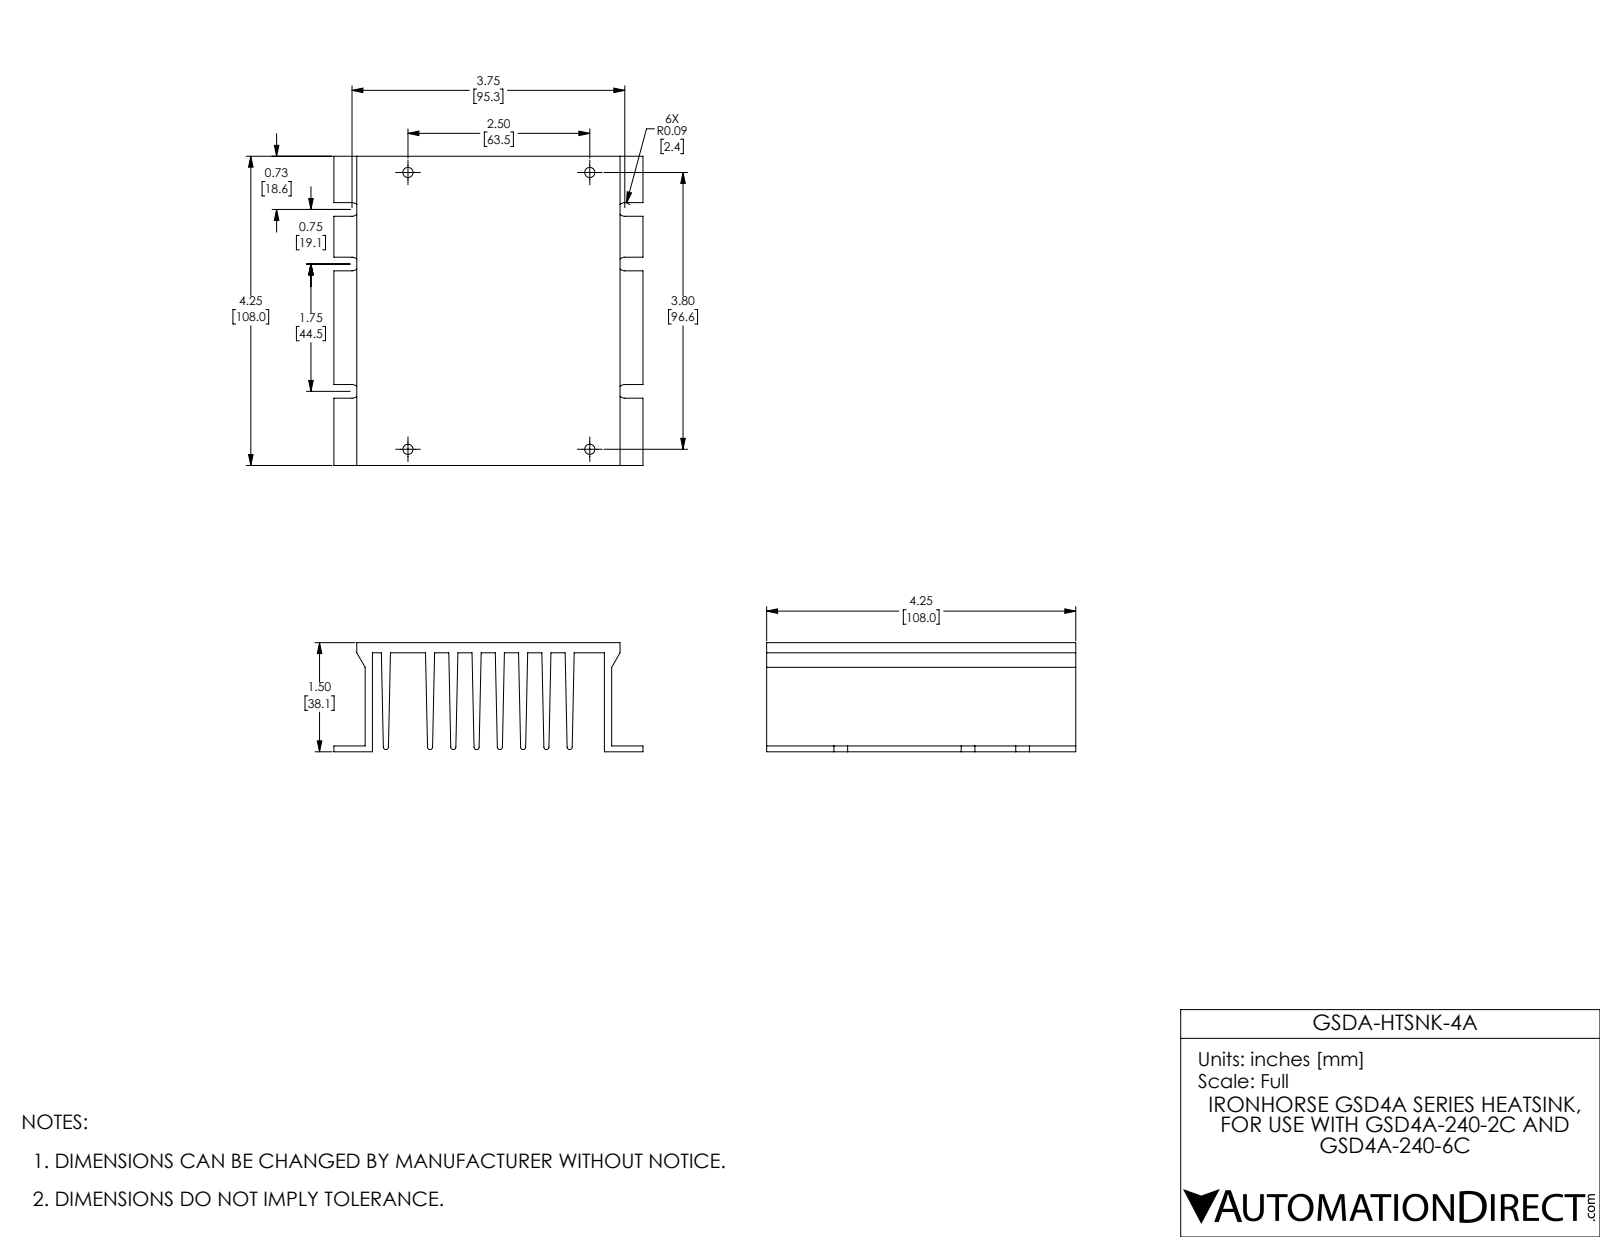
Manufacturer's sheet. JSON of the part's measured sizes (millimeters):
{"part_name": "GSDA-HTSNK-4A", "step_written_by": "SolidWorks 2017 (AUTOMOTIVE_DESIGN)", "units": "millimeters", "bodies": {"solids": 1, "faces": 83, "planar": 60, "cylindrical": 23, "other": 0}, "overall_size": [108, 108, 38.1], "volume_mm3": 131400, "surface_area_mm2": 98520, "round_holes": [[3.6, 4]], "partial_cylinders_radius": [[0.9, 8], [2.4, 6]], "face_to_face_distances": [8.1, 16.3, 24.4, 32.5, 16.3, 40.6, 24.4, 8.1, 15.4, 47.9], "hole_center_spacings": [63.5, 96.6, 115.6]}
